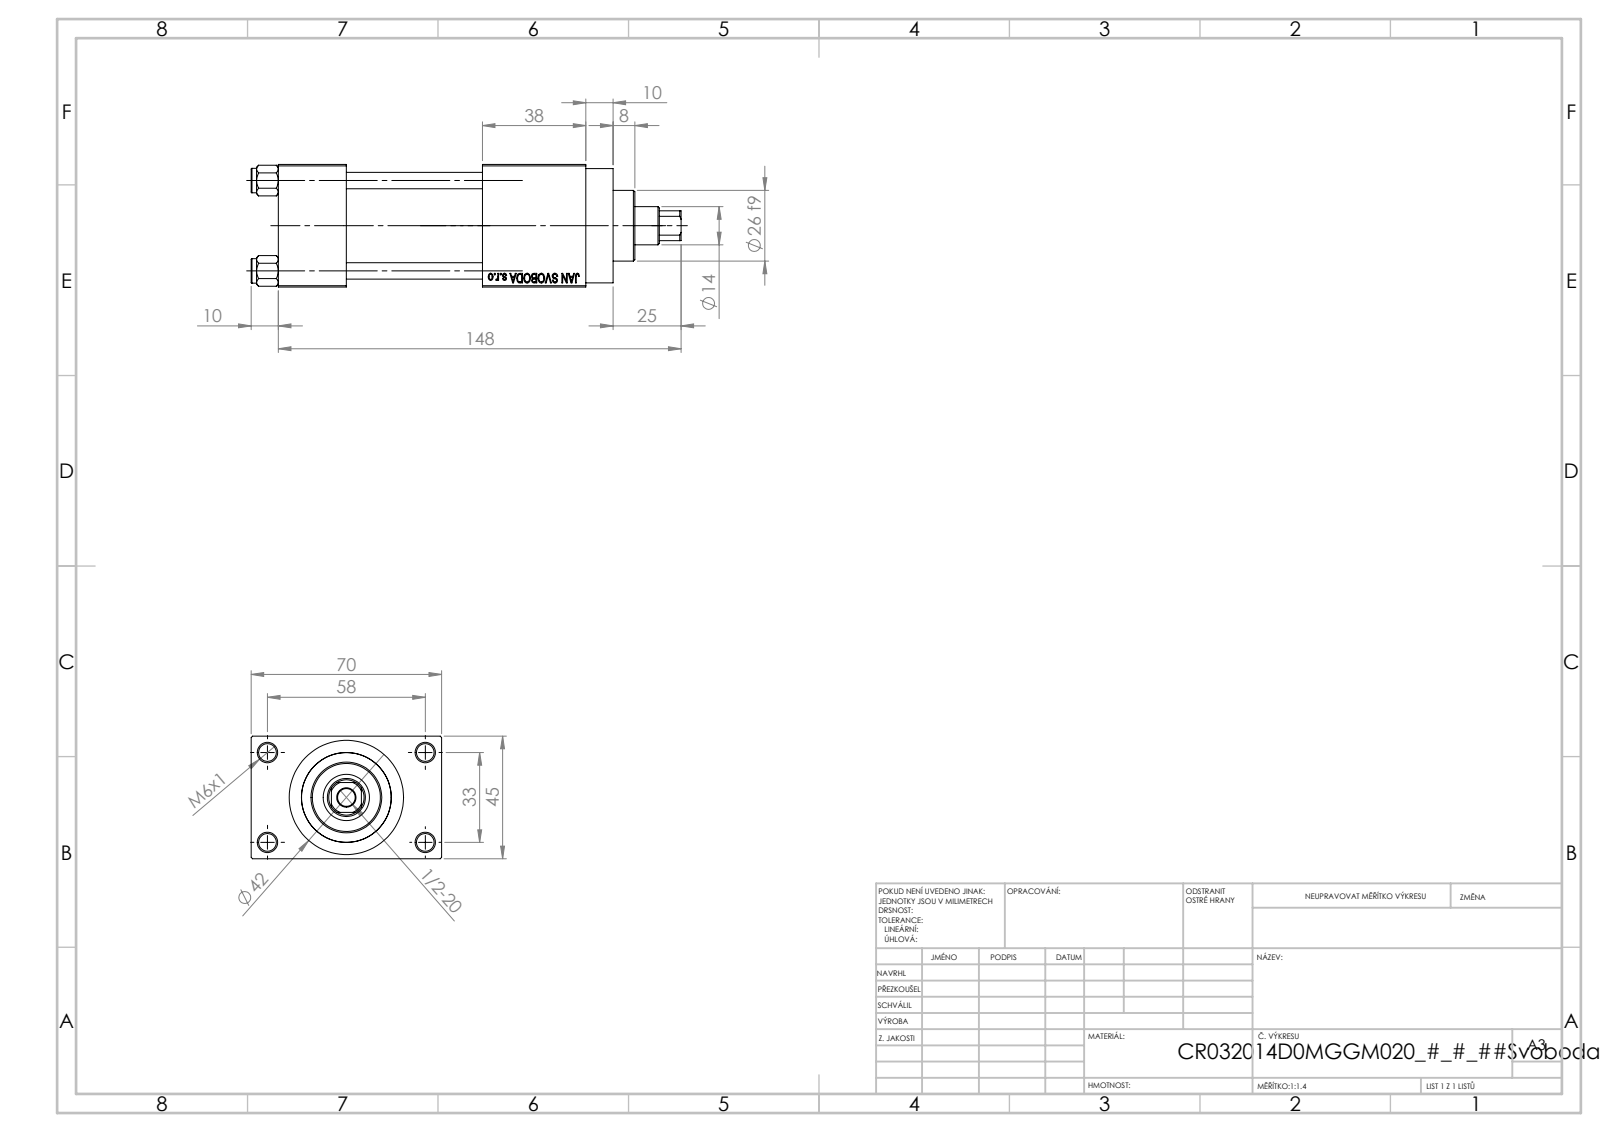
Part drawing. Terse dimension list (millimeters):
name: NUT_M5_D; V215CR_D_Body; V215_VC_A; V215CR_VCP_D (+1 more)
written by: SolidWorks 2019 (CONFIG_CONTROL_DESIGN)
unit: mm
bodies: 11 solids, 1103 faces (496 planar, 89 cylindrical, 518 other)
size: 158 × 70 × 45
volume: 231 947 mm³; area: 74 873 mm²
holes: 5× ⌀6.5, 4× ⌀6, 2× ⌀7, 2× ⌀13.16, 2× ⌀20, 1× ⌀14, 1× ⌀17, 1× ⌀24, 1× ⌀32, 1× ⌀33
bosses: 4× ⌀9, 1× ⌀42, 1× ⌀38, 1× ⌀26
rounds: 1× R6.5
face distances: 45, 25, 12.5, 57.5, 50, 75, 88, 70, 38, 113
hole spacings: 12.4, 23.48, 33.2, 33.37, 35.35, 45.6, 56.35, 33
